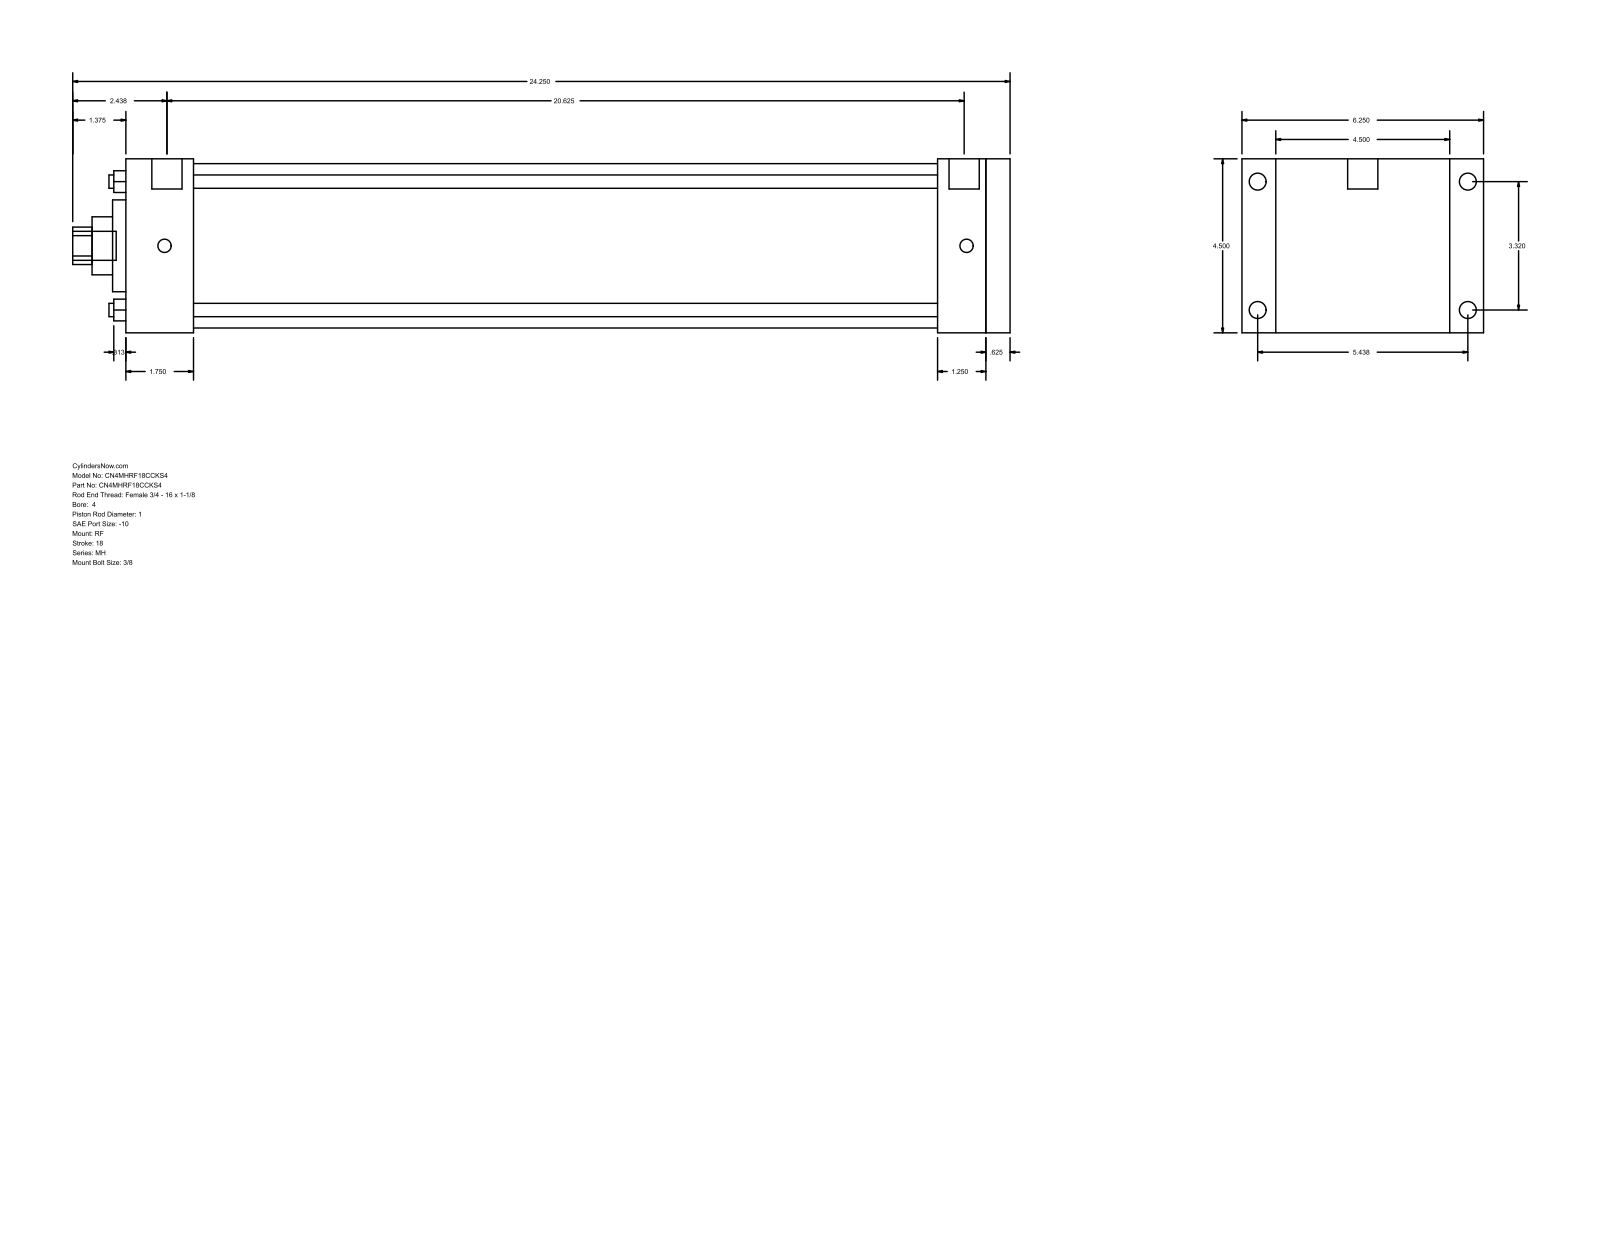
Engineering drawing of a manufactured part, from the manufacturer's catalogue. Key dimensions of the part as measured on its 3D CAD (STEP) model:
Part name (STEP PRODUCT): MH_RF__0400_1
STEP written by: GSSL Pune (CONFIG_CONTROL_DESIGN)
Units: millimetres
Bodies: 0 solids, 94 faces (65 planar, 29 cylindrical, 0 other)
Overall size (bounding box): 615.95 × 158.75 × 114.3
Round holes (diameter × count): ⌀8.76 ×4, ⌀25.4 ×1, ⌀38.1 ×1, ⌀60.33 ×1, ⌀107.95 ×1
Round bosses / shafts (diameter × count): ⌀11.13 ×4, ⌀8.73 ×4, ⌀19.84 ×2, ⌀19.05 ×1
Partial cylindrical surfaces — rounded edges, fillets, slot ends (radius × count): R12.29 ×1
Main face-to-face distances: 114.3, 581.03, 15.87, 565.16, 44.46, 520.7, 536.57, 533.41, 488.95, 31.75
Hole centre spacings: 59.62, 84.32, 119.25
